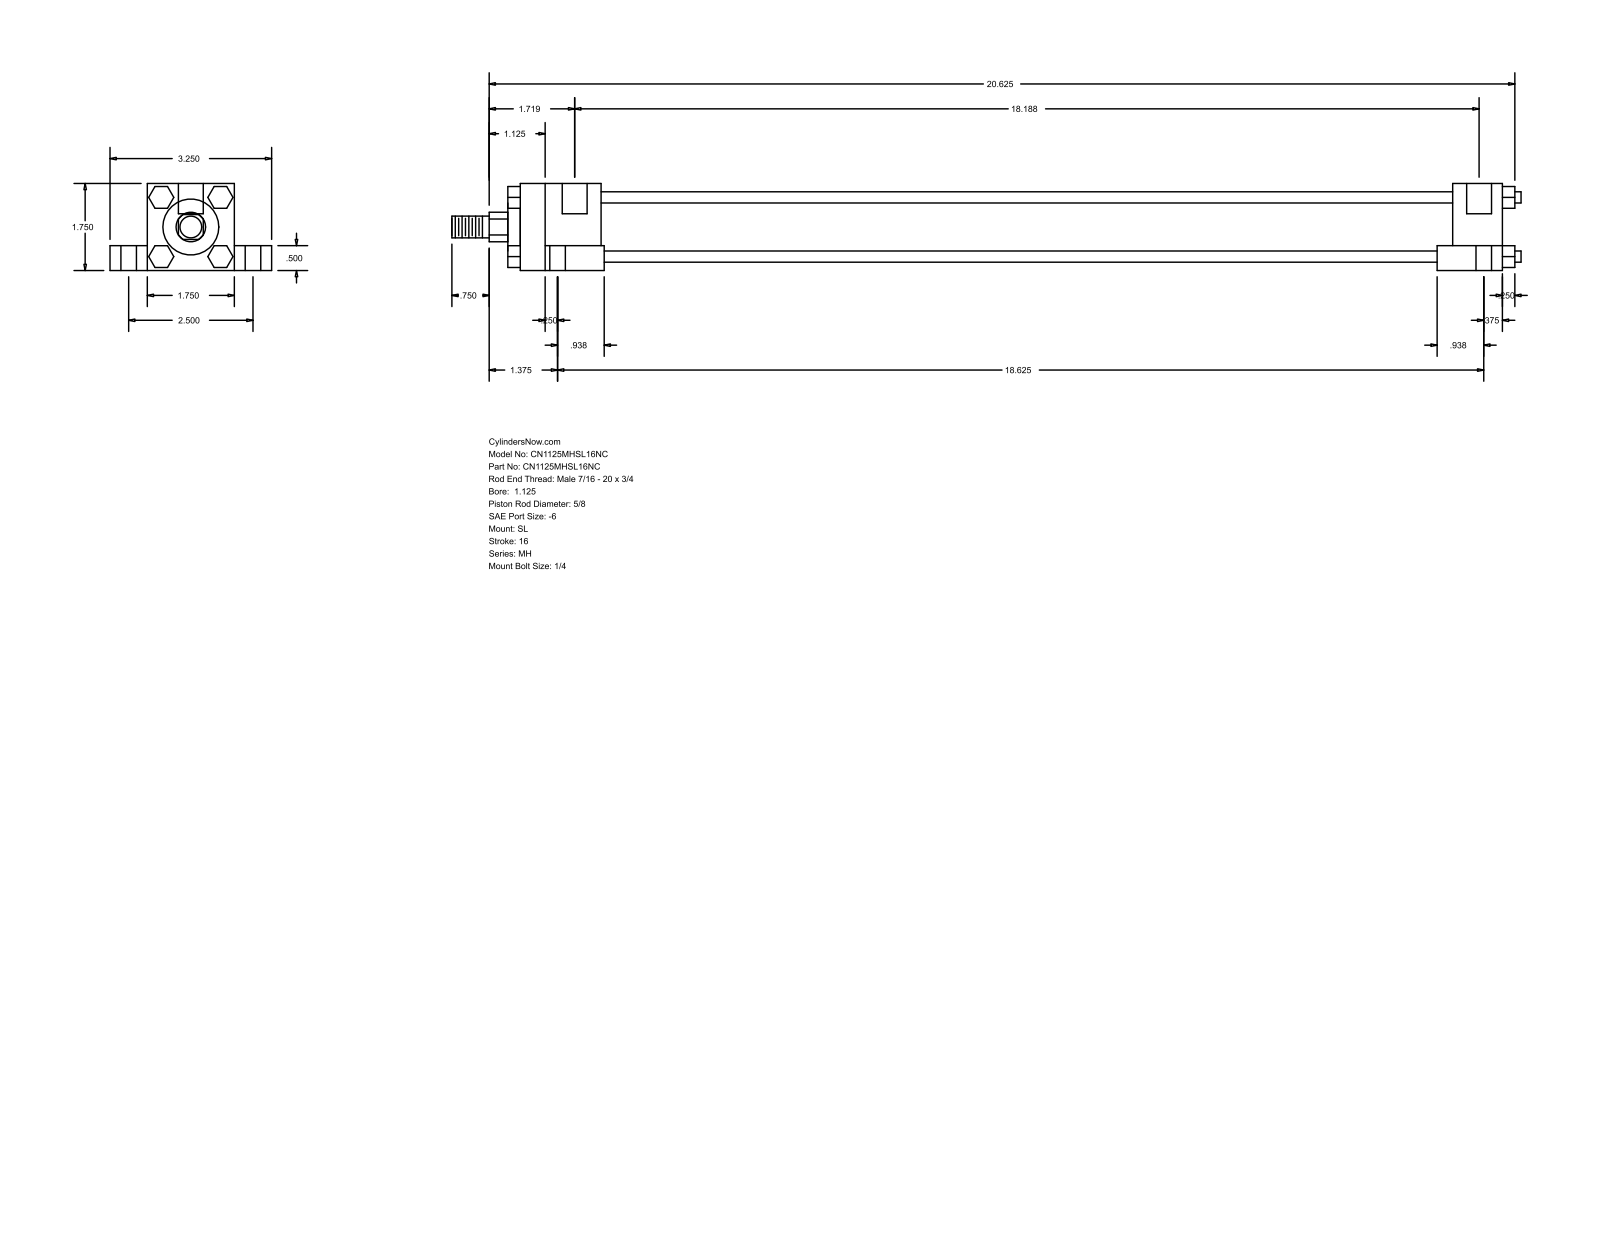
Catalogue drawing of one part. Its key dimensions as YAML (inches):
part_name: "MH_SL__0112_0.625"
step_written_by: "GSSL Pune (CONFIG_CONTROL_DESIGN)"
units: inches
bodies: {solids: 0, faces: 150, planar: 114, cylindrical: 36, other: 0}
overall_size: [21.5, 3.25, 1.75]
round_holes:
  - {diameter: 0.219, count: 4}
  - {diameter: 0.313, count: 4}
  - {diameter: 0.563, count: 4}
  - {diameter: 0.5, count: 2}
round_bosses_or_shafts:
  - {diameter: 0.225, count: 4}
  - {diameter: 1.375, count: 1}
  - {diameter: 1.125, count: 1}
  - {diameter: 0.625, count: 1}
  - {diameter: 0.437, count: 1}
partial_cylinders:
  - {radius: 0.297, count: 1}
face_to_face_distances: [1.75, 1.25, 0.75, 0.5, 2.5, 0.437, 1.875, 1, 17.125, 18.125]
hole_center_spacings: [1.254, 1.269, 1.296, 2.5, 18.063, 18.199, 18.324, 18.449]
